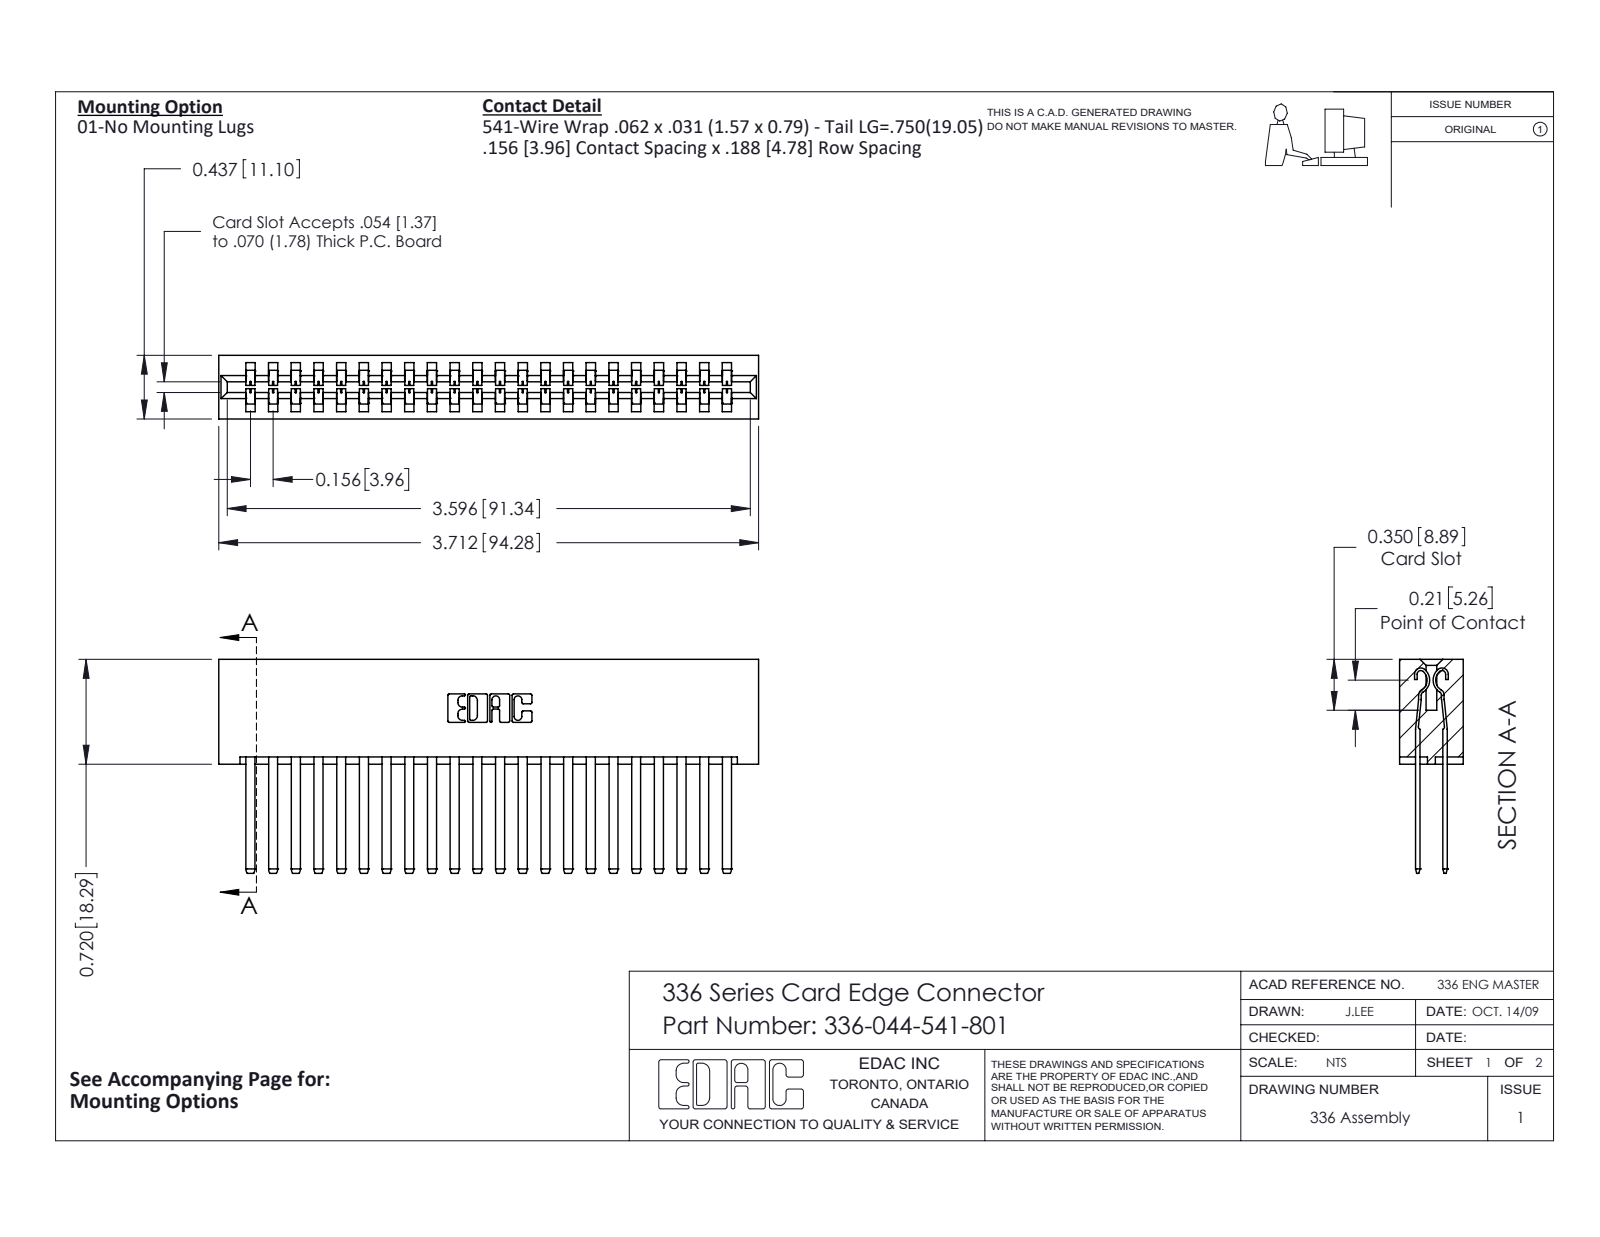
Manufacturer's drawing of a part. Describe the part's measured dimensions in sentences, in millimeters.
The part is named "336-044-541-801; 336-290-001_336-290-541; 336 Part_Lugless". Its 3-D file was written by "SolidWorks 2020 (CONFIG_CONTROL_DESIGN)". It is 45 solids with 1954 faces: 1210 planar, 744 cylindrical and 0 other. Overall it measures 94.3 by 37.3 by 11.1 millimeters. Its volume is 15 600 cubic millimeters and its surface area 19 720 square millimeters. Partial cylindrical surfaces (rounded edges, fillets, slot ends): 88 of radius 0.1, 44 of radius 1.4, 22 of radius 0.3, 6 of radius 0.2, 6 of radius 0.8, 4 of radius 0.6, 4 of radius 1, 3 of radius 0.7. The main face-to-face distances are 4.8, 8.3, 3.6, 7.5, 2.8, 0.8, 11.1, 0.8, 4, 4.6.
